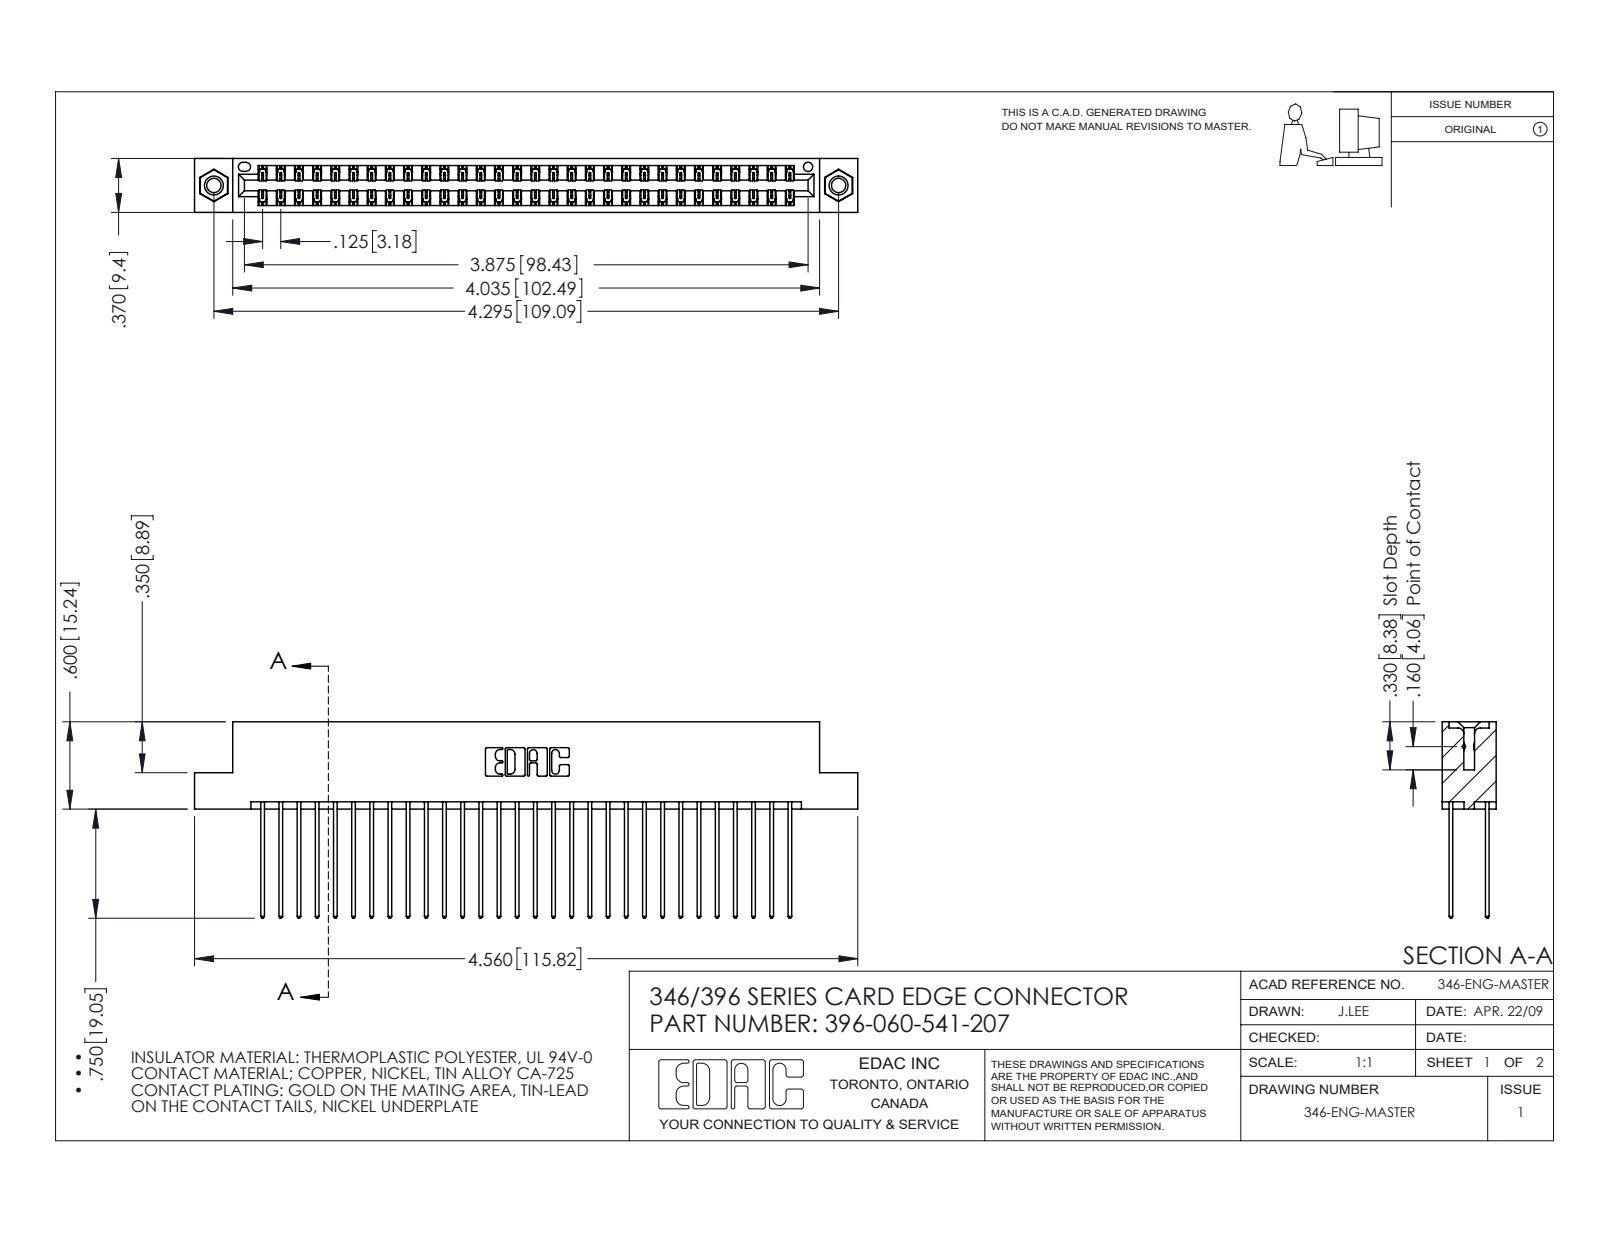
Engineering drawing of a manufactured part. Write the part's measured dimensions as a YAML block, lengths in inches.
part_name: "396-060-541-207; 346 Part_Flush Mounting Lugs - 0.156 Dia-TI; 345-292-001_345-293-141; 345-250-001_345-250-005-103"
step_written_by: "SolidWorks 2016 (CONFIG_CONTROL_DESIGN)"
units: inches
bodies: {solids: 63, faces: 3302, planar: 2208, cylindrical: 1078, other: 16}
overall_size: [4.56, 1.35, 0.37]
volume: 0.704
surface_area: 26.89
round_holes:
  - {diameter: 0.098, count: 2}
  - {diameter: 0.125, count: 2}
  - {diameter: 0.156, count: 2}
  - {diameter: 0.064, count: 1}
round_bosses_or_shafts:
  - {diameter: 0.155, count: 2}
partial_cylinders:
  - {radius: 0.006, count: 90}
  - {radius: 0.01, count: 60}
  - {radius: 0.01, count: 22}
  - {radius: 0.007, count: 6}
  - {radius: 0.031, count: 6}
  - {radius: 0.026, count: 3}
  - {radius: 0.014, count: 2}
  - {radius: 0.022, count: 2}
face_to_face_distances: [0.048, 0.322, 0.25, 0.072, 0.298, 0.025, 0.37, 0.275, 0.225, 0.148]
hole_center_spacings: [0.246, 4.087, 4.295]
